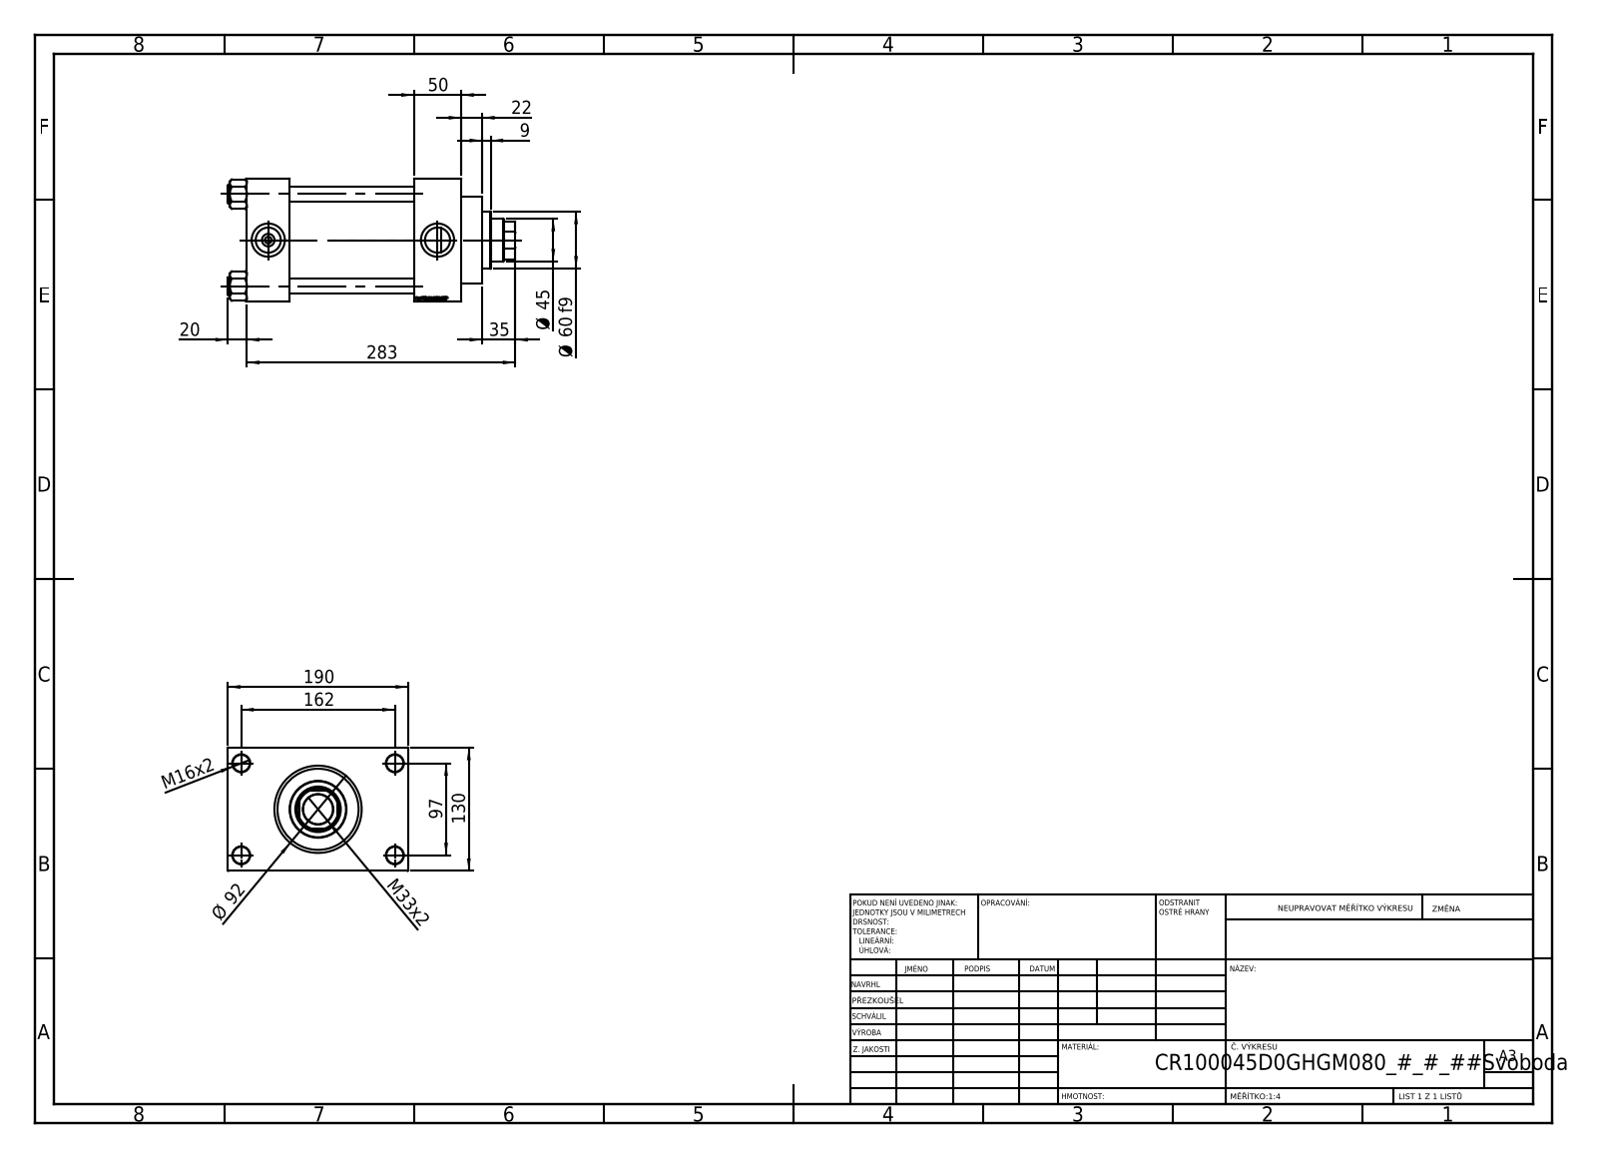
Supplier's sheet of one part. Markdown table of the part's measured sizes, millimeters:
| quantity | value |
| --- | --- |
| part name | NUT_M5_D; V215CR_D_Body; V215_VC_A; V215CR_VCP_D (+1 more) |
| STEP written by | SolidWorks 2019 (CONFIG_CONTROL_DESIGN) |
| units | millimeters |
| bodies | 11 solids, 1151 faces (545 planar, 88 cylindrical, 518 other) |
| overall size | 303 × 190 × 130 |
| volume | 2 792 000 mm³ |
| surface area | 414 253 mm² |
| round holes (diameter × count) | 16 × 4, 18 × 4, 7 × 2, 26.44 × 2, 35 × 2, 31.5 × 1, 45 × 1, 48 × 1, 76 × 1, 85.5 × 1, 100 × 1 |
| round bosses / shafts (diameter × count) | 19 × 4, 106 × 1, 92 × 1, 60 × 1 |
| partial cylindrical surfaces (radius × count) | 22 × 1 |
| main face-to-face distances | 130, 45, 176, 131, 226, 181, 50, 30, 160, 80 |
| hole center spacings | 32.55, 68.52, 94.41, 96.9, 102.27, 129.45, 161.73, 97 |
